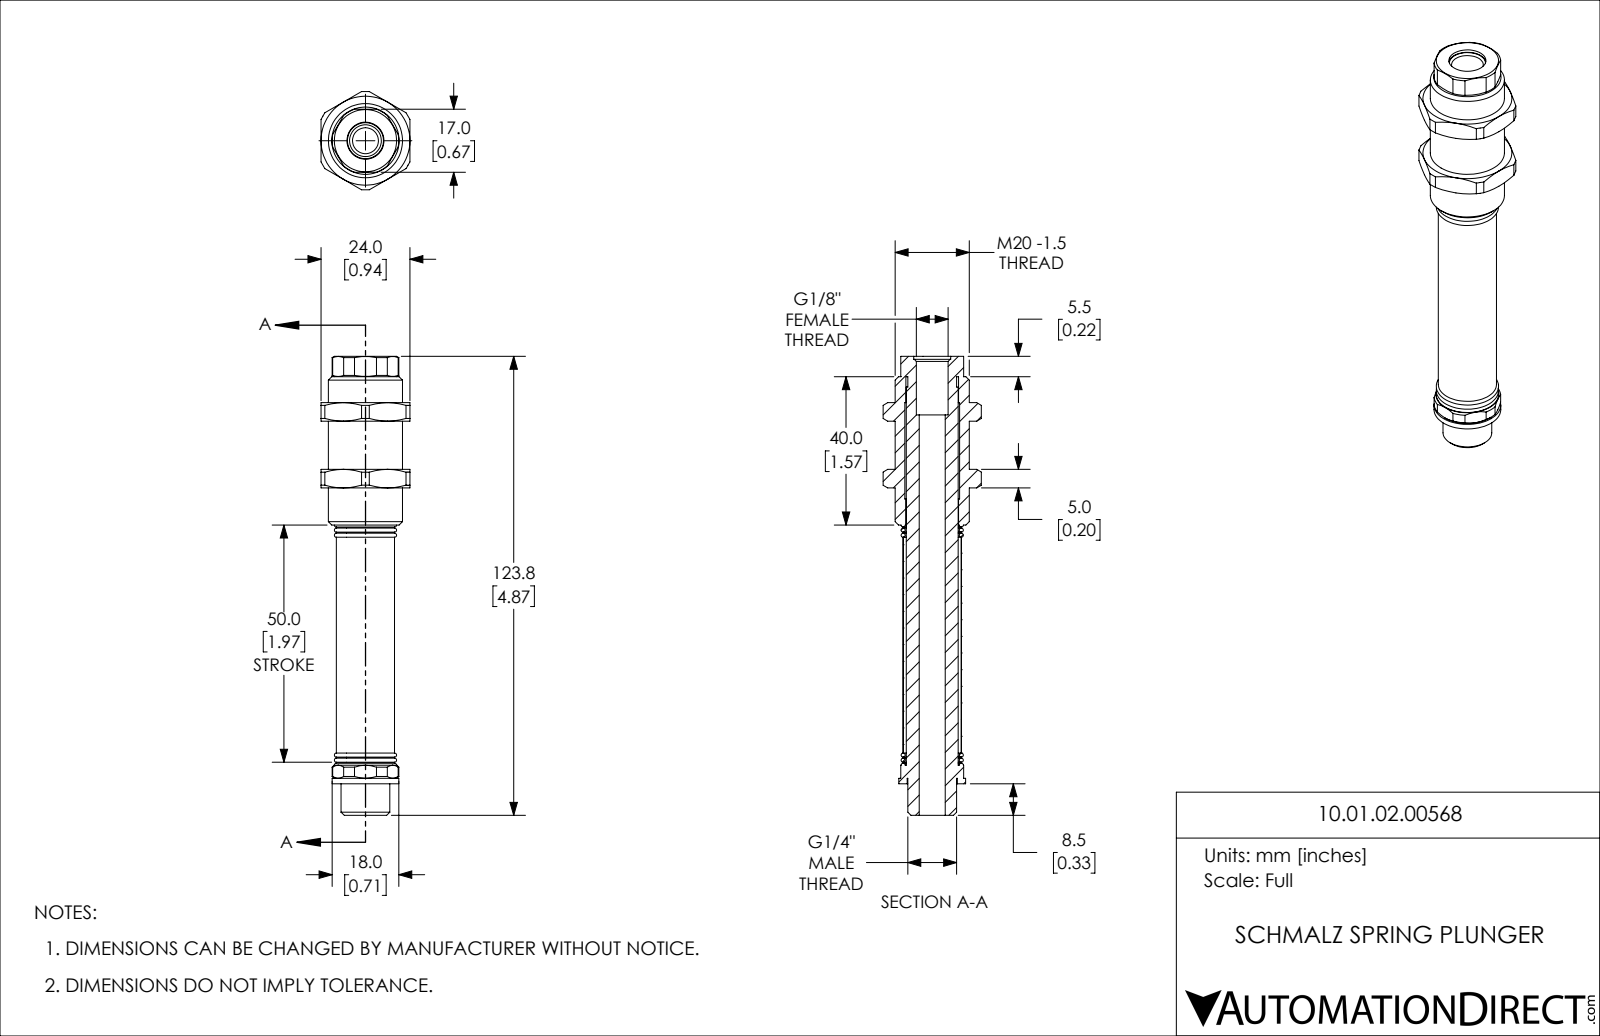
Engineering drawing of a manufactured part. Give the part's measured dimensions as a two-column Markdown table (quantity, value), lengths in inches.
| quantity | value |
| --- | --- |
| part name | 10.01.02.00568 |
| STEP written by | SolidWorks 2021 (CONFIG_CONTROL_DESIGN) |
| units | inches |
| bodies | 1 solid, 200 faces (56 planar, 60 cylindrical, 84 other) |
| overall size | 4.874 × 1.044 × 0.945 |
| volume | 1.373 in³ |
| surface area | 32.53 in² |
| round holes (diameter × count) | 0.276 × 1, 0.337 × 1, 0.394 × 1, 0.531 × 1, 0.559 × 1, 0.583 × 1, 0.618 × 1 |
| round bosses / shafts (diameter × count) | 0.787 × 1, 0.709 × 1, 0.618 × 1, 0.551 × 1, 0.518 × 1 |
| main face-to-face distances | 0.945, 0.197, 0.709, 0.669, 0.492, 1.201, 0.906, 1.398, 0.512, 0.689 |
